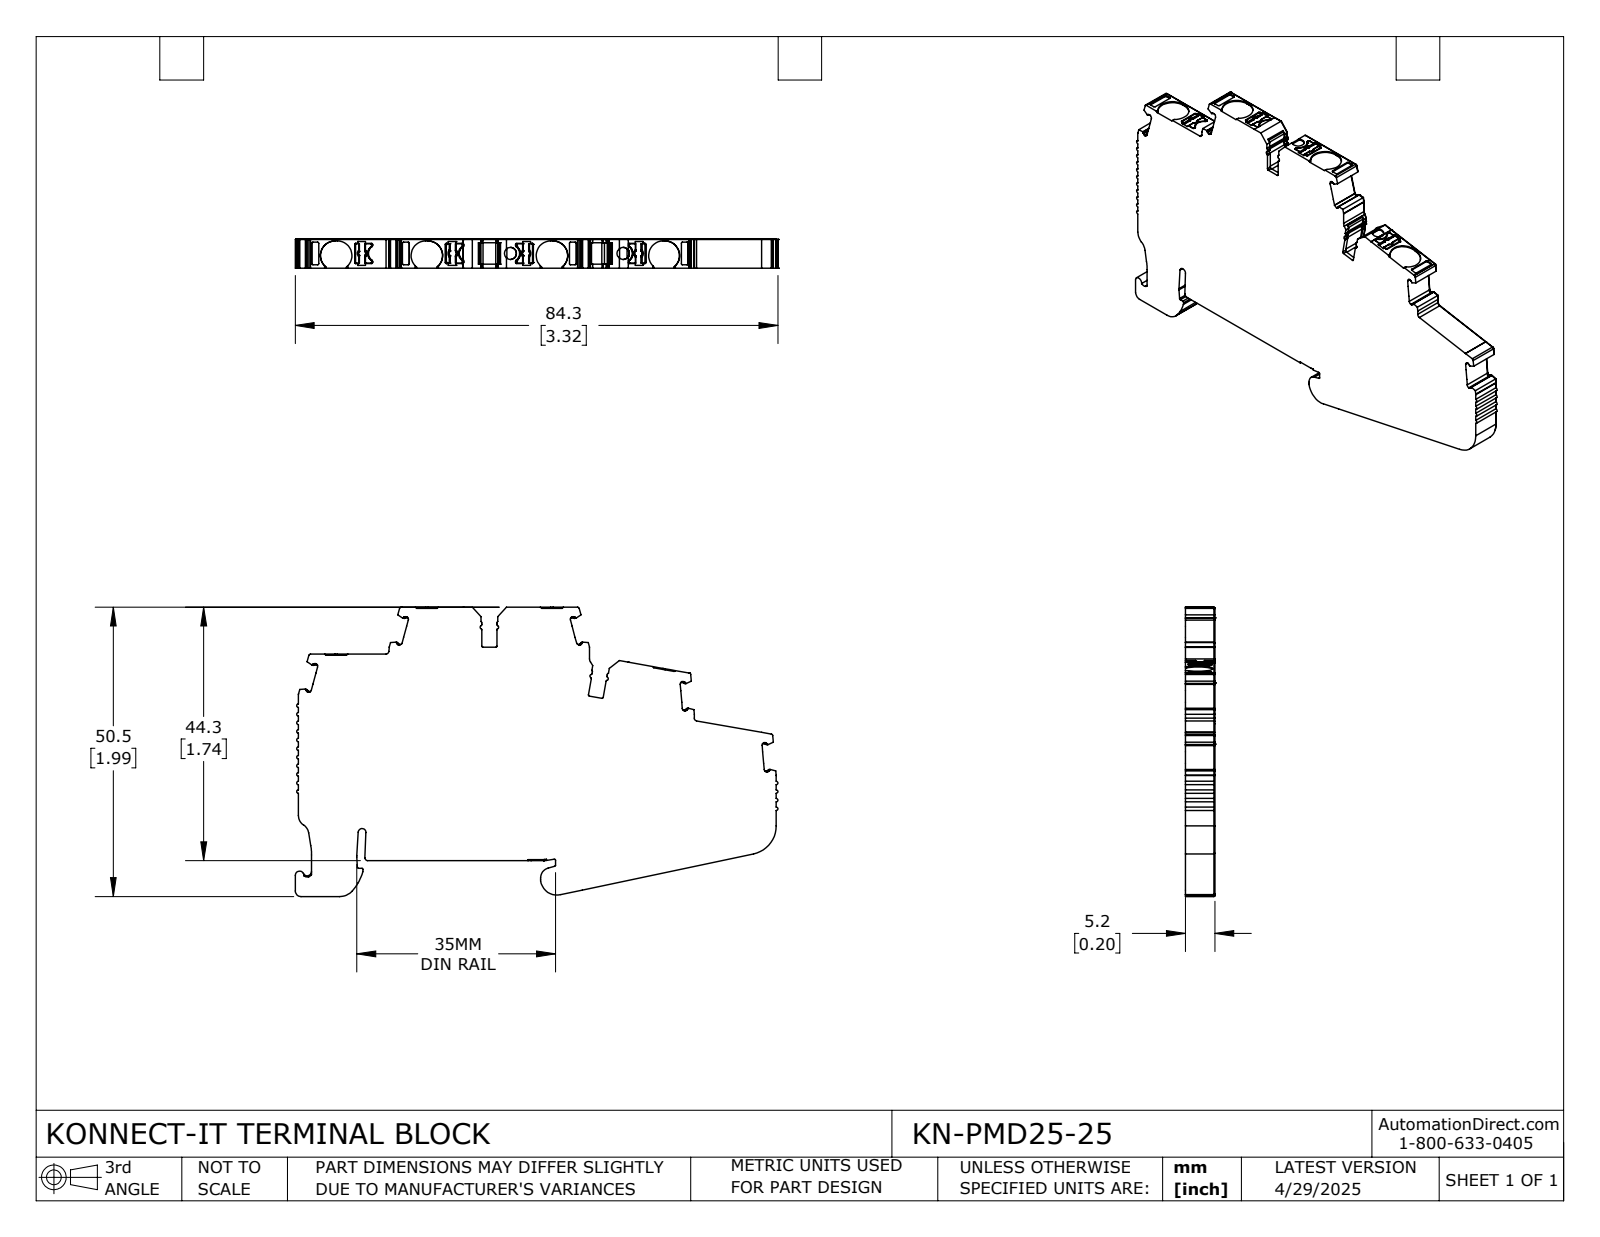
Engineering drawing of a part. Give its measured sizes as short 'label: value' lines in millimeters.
name: KN-PMD25-25
written by: SolidWorks 2024 (CONFIG_CONTROL_DESIGN)
unit: mm
bodies: 1 solid, 903 faces (446 planar, 390 cylindrical, 67 other)
size: 84.28 × 50.52 × 5.15
volume: 15 859 mm³; area: 7 937 mm²
holes: 2× ⌀2.1
rounds: 85× R0.2, 47× R0.3, 31× R0.1, 21× R0.5, 16× R0.15, 12× R0.6, 10× R0.16, 10× R0.26
face distances: 5.15, 8.19, 8.18, 2, 44.06, 35.87, 44.05, 6.26, 50.32, 5
